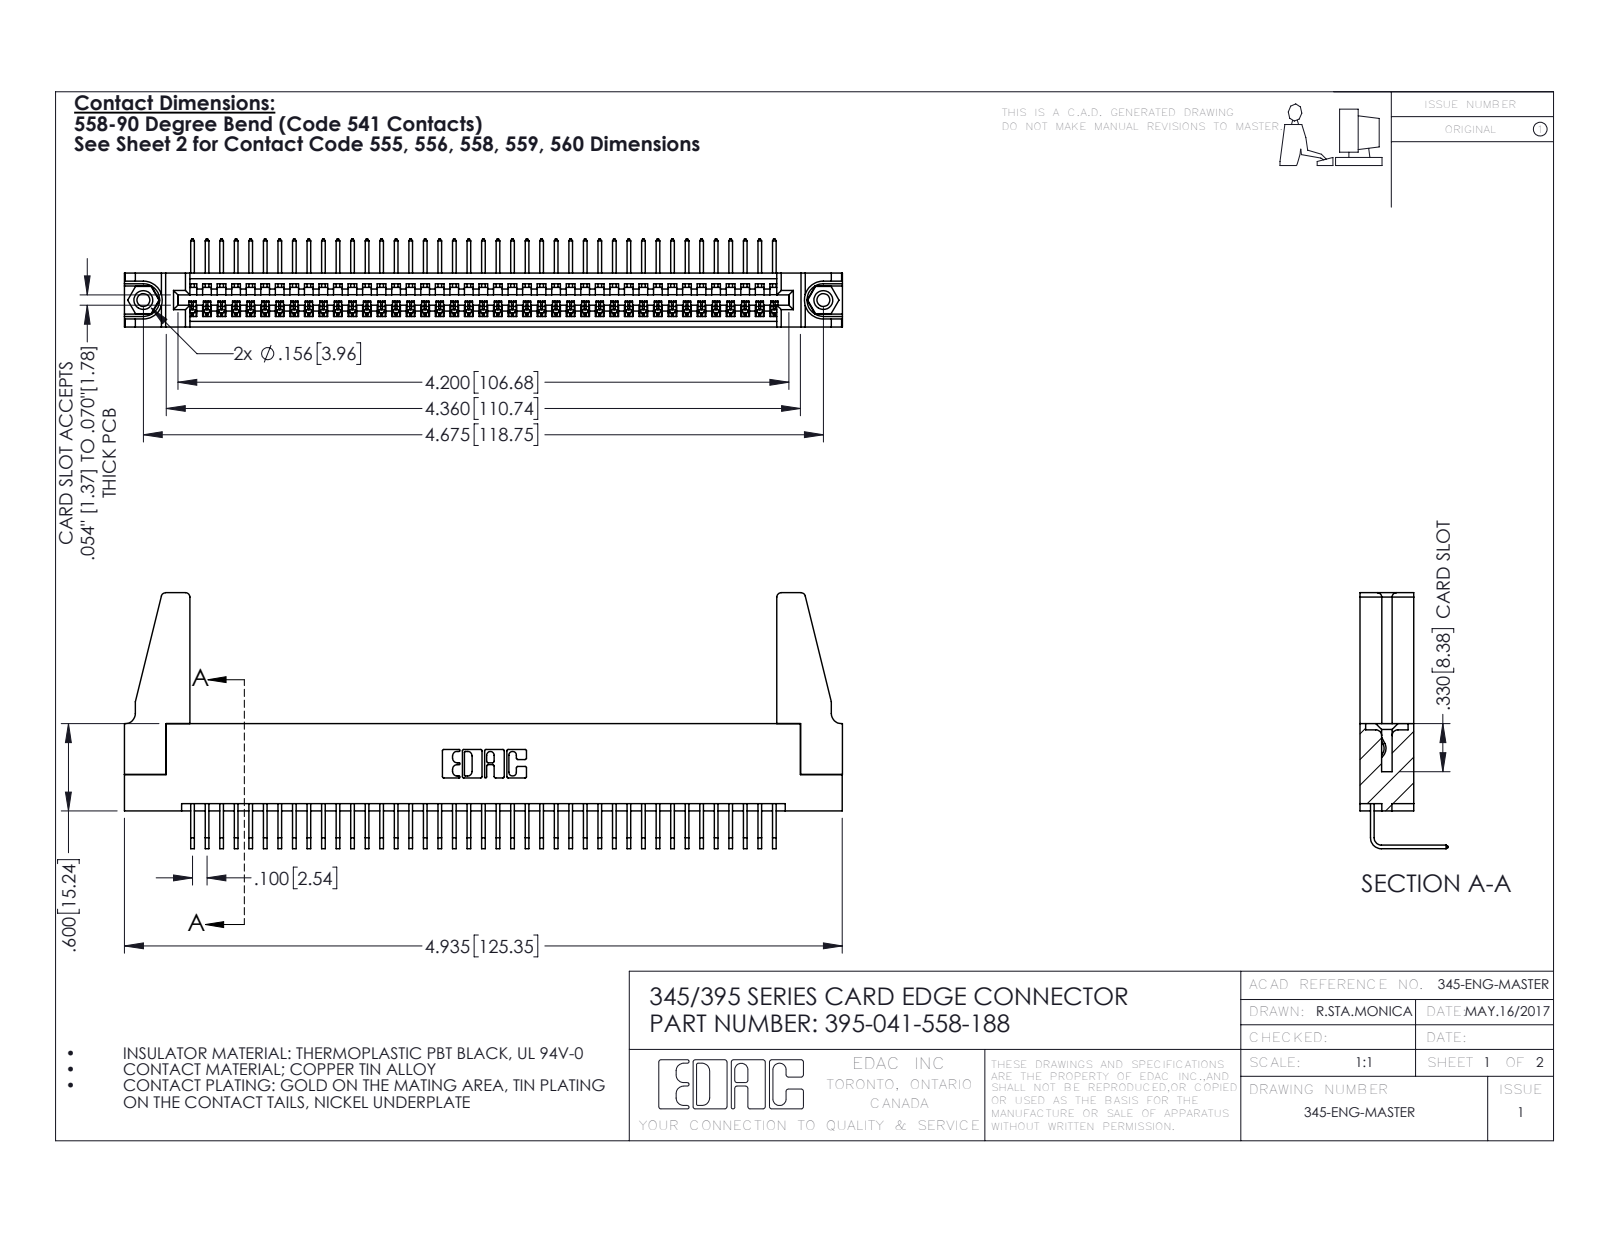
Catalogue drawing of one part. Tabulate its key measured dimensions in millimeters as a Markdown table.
| quantity | value |
| --- | --- |
| part name | 345-250-001_345-250-001-102; 345-292-001_558 Tail - 2; 345 Part_Flush Mounting Lugs - 0.156 Dia-TH; 345-220-078_345-220-088 (+1 more) |
| STEP written by | SolidWorks 2016 (CONFIG_CONTROL_DESIGN) |
| units | millimeters |
| bodies | 46 solids, 2710 faces (1874 planar, 820 cylindrical, 16 other) |
| overall size | 125.4 × 44.7 × 15.4 |
| volume | 15 300 mm³ |
| surface area | 19 920 mm² |
| round holes (diameter × count) | 2.3 × 2, 3.2 × 2, 4 × 2, 1.6 × 1 |
| round bosses / shafts (diameter × count) | 3.9 × 2 |
| partial cylindrical surfaces (radius × count) | 0.2 × 82, 0.3 × 22, 0.8 × 8, 0.2 × 6, 0.8 × 6, 0.7 × 3, 0.8 × 2, 1 × 2 |
| main face-to-face distances | 1.8, 7.6, 9.4, 5.1, 2.5, 6.9, 0.6, 5.7, 3.8, 1.8 |
| hole center spacings | 6.9, 112.8, 118.7 |
